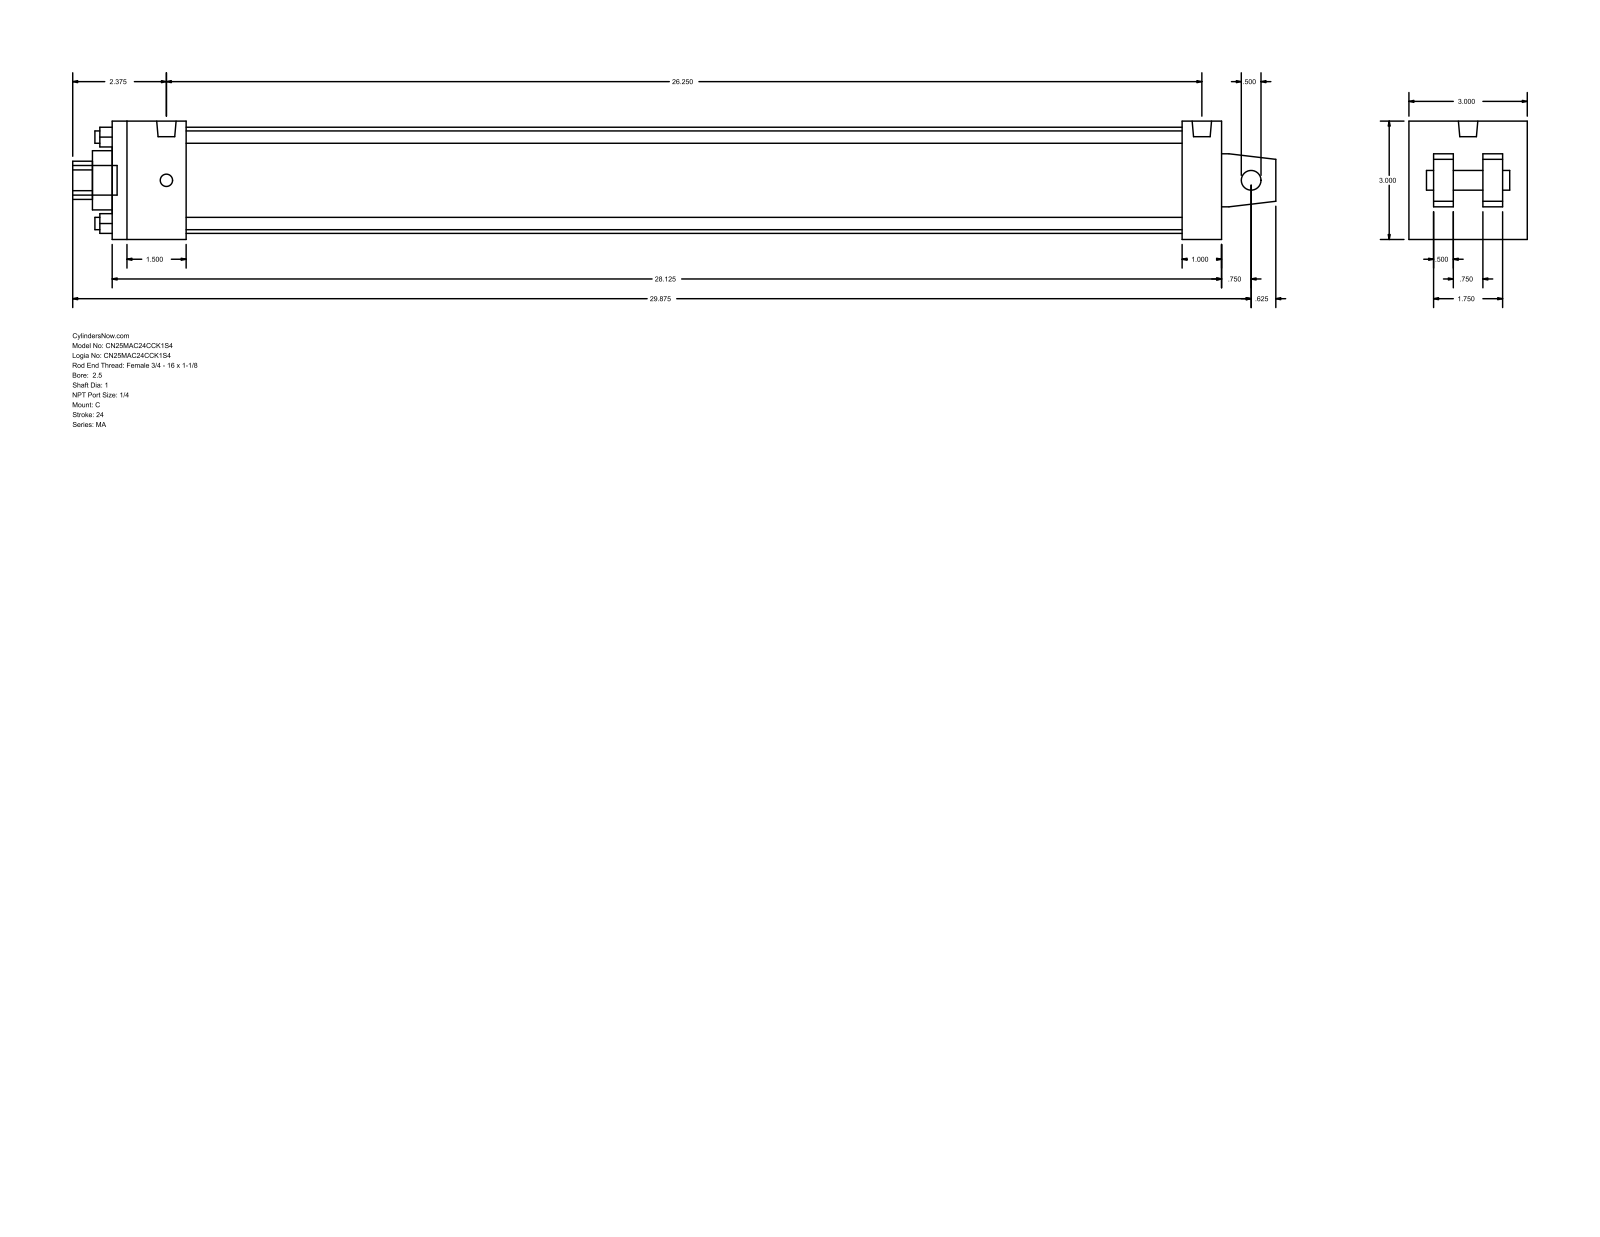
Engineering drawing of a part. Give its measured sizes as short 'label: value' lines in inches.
name: MA_C__0250_1
written by: GSSL Pune (CONFIG_CONTROL_DESIGN)
unit: in
bodies: 0 solids, 103 faces (76 planar, 27 cylindrical, 0 other)
size: 30.5 × 3 × 3
holes: 4× ⌀0.313, 1× ⌀0.5, 1× ⌀1, 1× ⌀1.5, 1× ⌀2.69
bosses: 4× ⌀0.313, 2× ⌀0.492, 1× ⌀0.75
rounds: 1× R0.484
face distances: 3, 1.875, 28.125, 0.5, 0.625, 2.375, 1.125, 27.125, 25.25, 26.25
hole spacings: 1.548, 2.19, 3.097
